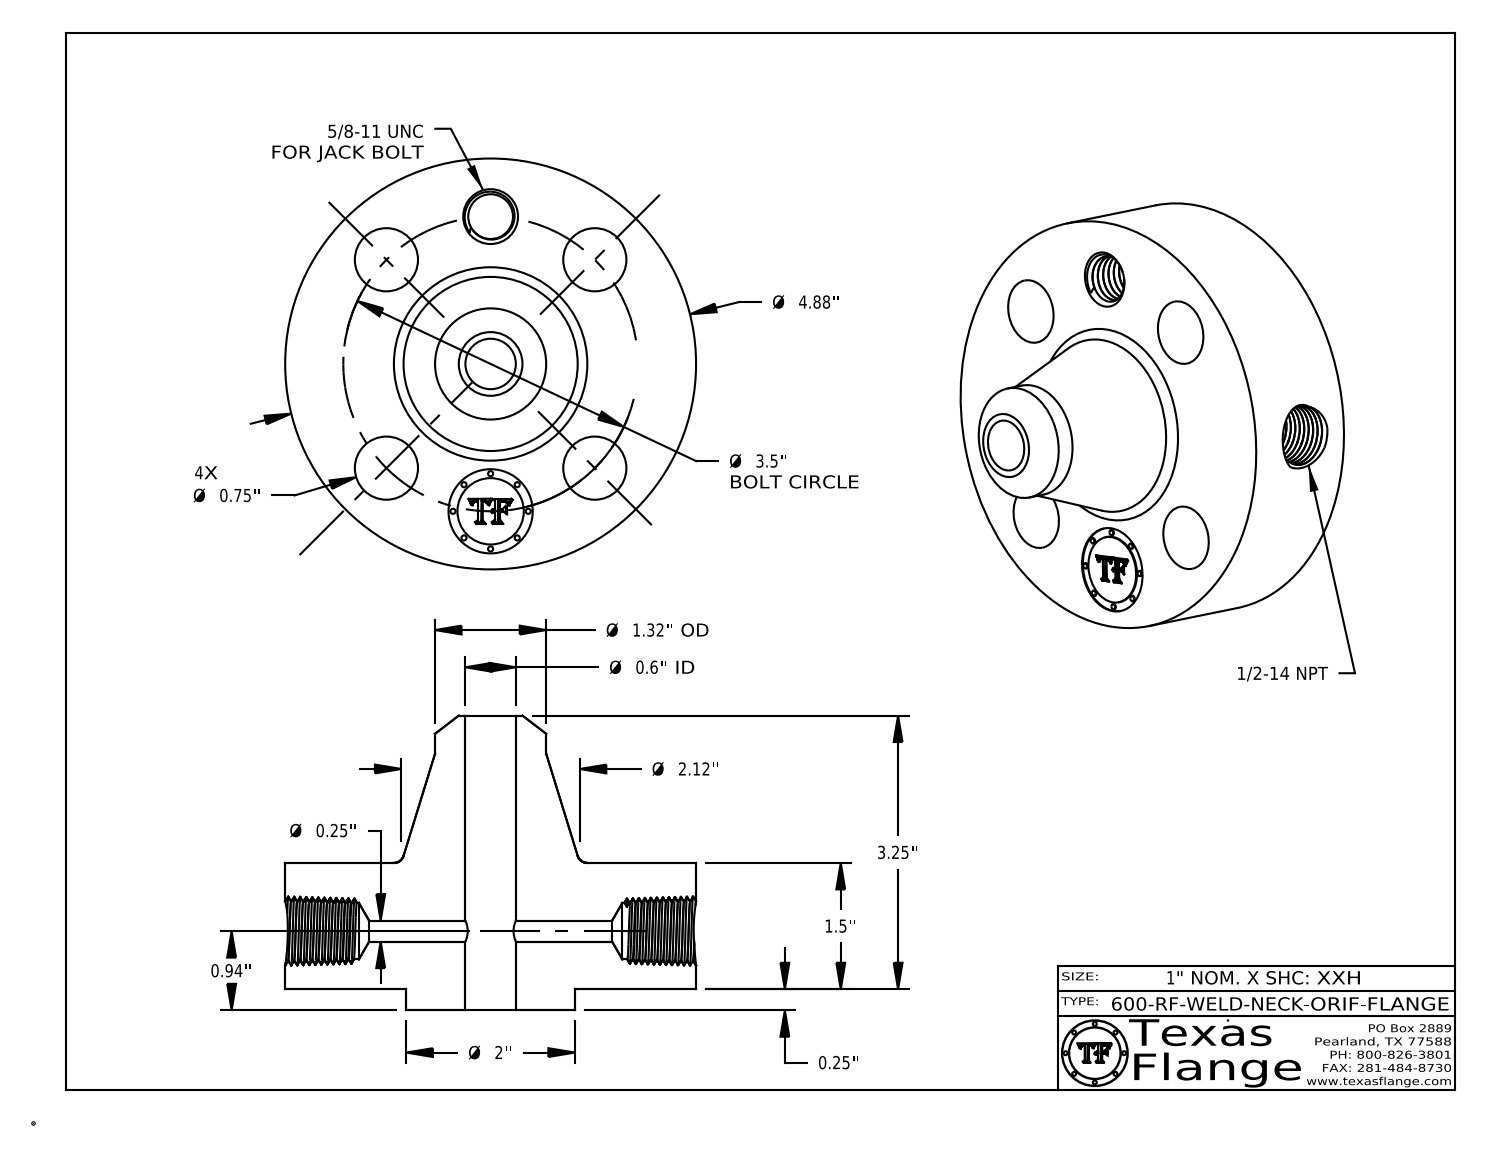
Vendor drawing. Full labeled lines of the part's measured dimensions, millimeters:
Part name (STEP PRODUCT): 600-RF-WELD-NECK
STEP written by: CATIA V5 STEP AP214 (AUTOMOTIVE_DESIGN)
Units: millimetres
Bodies: 1 solid, 764 faces (369 planar, 87 cylindrical, 308 other)
Overall size (bounding box): 124 × 124 × 88.9
Volume: 450 600 mm³ · Surface area: 62 560 mm²
Round holes (diameter × count): ⌀19.1 ×4, ⌀6.4 ×1, ⌀13.5 ×1, ⌀15.2 ×1, ⌀17.1 ×1, ⌀25.4 ×1
Round bosses / shafts (diameter × count): ⌀1.5 ×8, ⌀124 ×1, ⌀50.8 ×1, ⌀33.5 ×1, ⌀20 ×1
Main face-to-face distances: 38.1, 44.5, 6.4, 44.1, 37.7, 0.4, 88.9, 82.6, 44.8, 7.6
Hole centre spacings: 44.5, 34, 62.9, 82.1, 88.9
